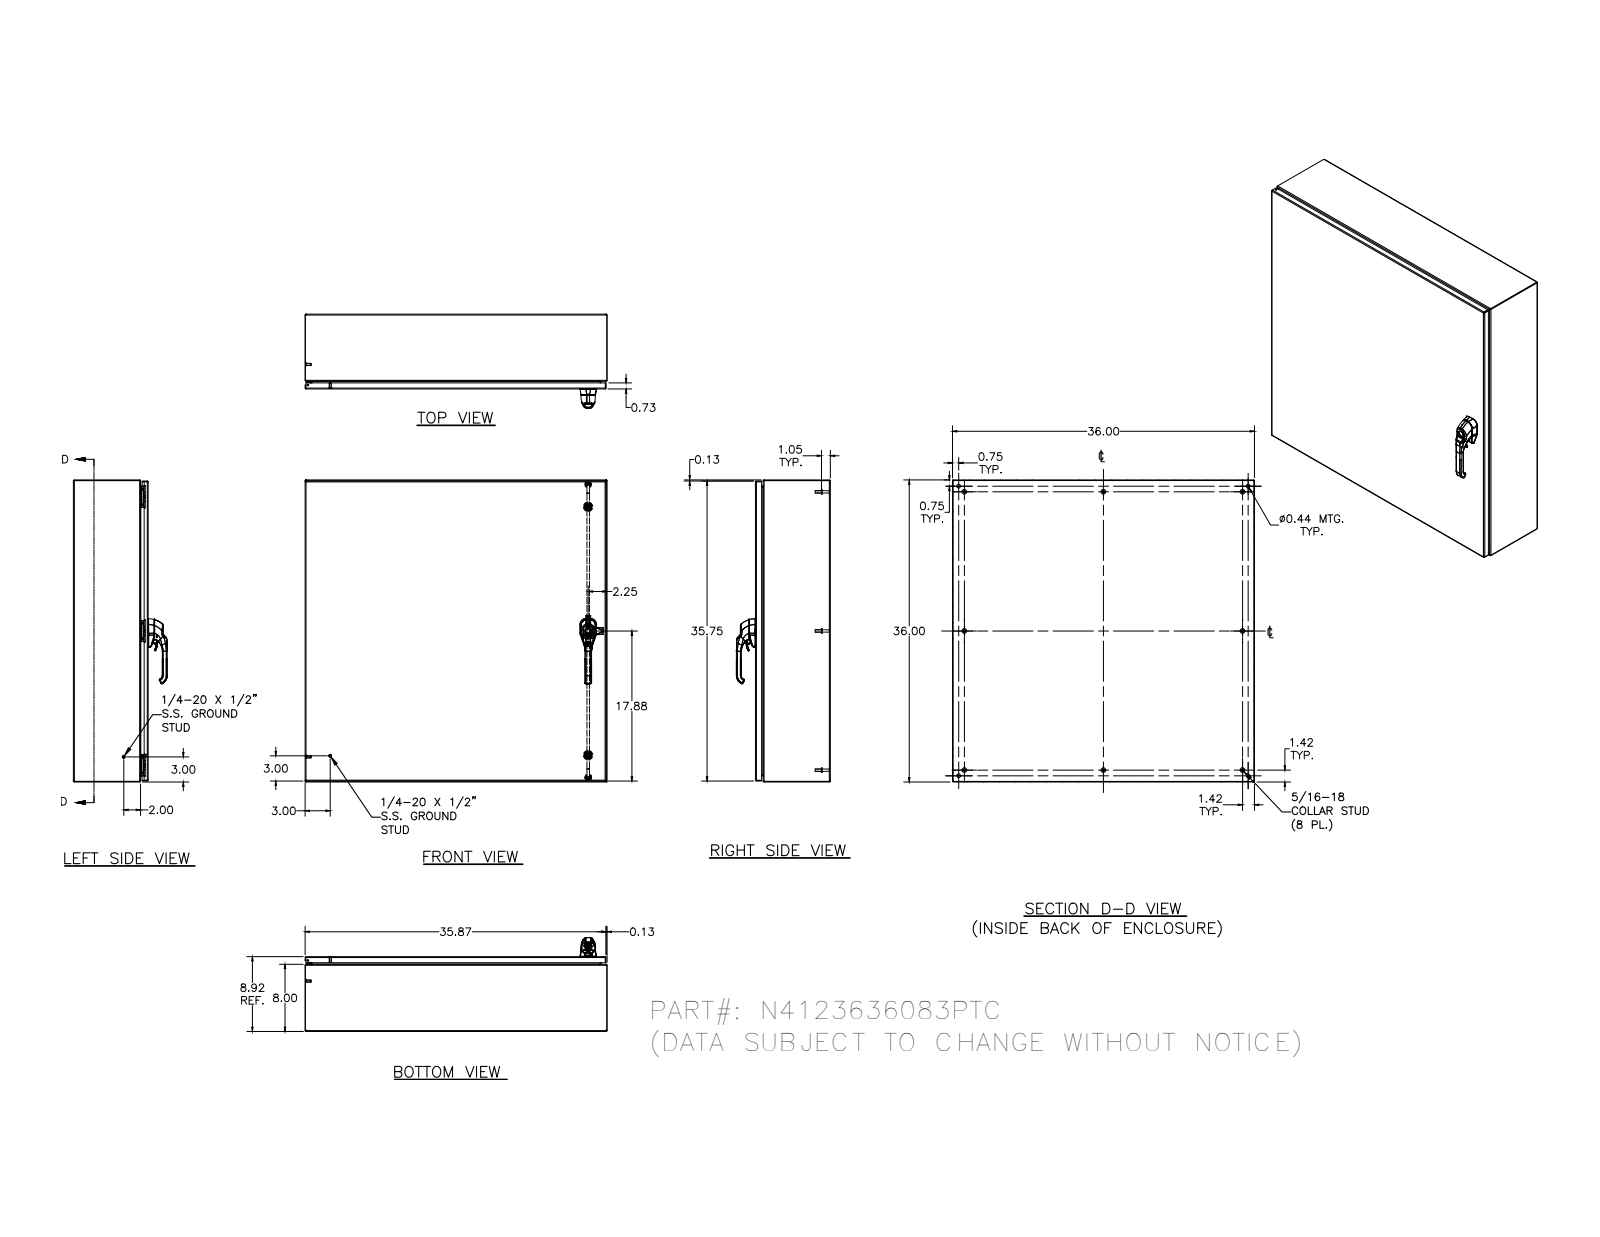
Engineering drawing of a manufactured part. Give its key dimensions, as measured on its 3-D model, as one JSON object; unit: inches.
{"part_name": "N4123636083PTC; N4123636083PTCBKP; N41236363PTCLID; HFW328176 (+8 more)", "step_written_by": "Autodesk Inventor 2011 (AUTOMOTIVE_DESIGN)", "units": "inches", "bodies": {"solids": 62, "faces": 3414, "planar": 1074, "cylindrical": 1285, "other": 1055}, "overall_size": [36, 36, 11.186], "volume_in3": 302.6, "surface_area_in2": 8254, "round_holes": [[0.188, 7], [0.093, 6], [0.152, 6], [0.167, 6], [0.172, 6], [0.165, 4], [0.197, 4], [0.437, 4], [0.156, 3], [0.213, 3], [0.236, 3], [0.354, 3]], "round_bosses_or_shafts": [[0.25, 14], [0.563, 8], [0.3, 8], [0.275, 8], [0.36, 6], [0.32, 6], [0.256, 6], [0.164, 6]], "partial_cylinders_radius": [[0.02, 179], [0.012, 80], [0.05, 38], [0.031, 34], [0.118, 32], [0.016, 26], [0.125, 21], [0.105, 20]], "face_to_face_distances": [0.074, 8.843, 8.769, 8.917, 35.926, 35.852, 36, 7.926, 0.917, 0.739], "hole_center_spacings": [16, 15.996, 16.008, 31.996, 0.017, 0.66, 16.004, 16.656]}
